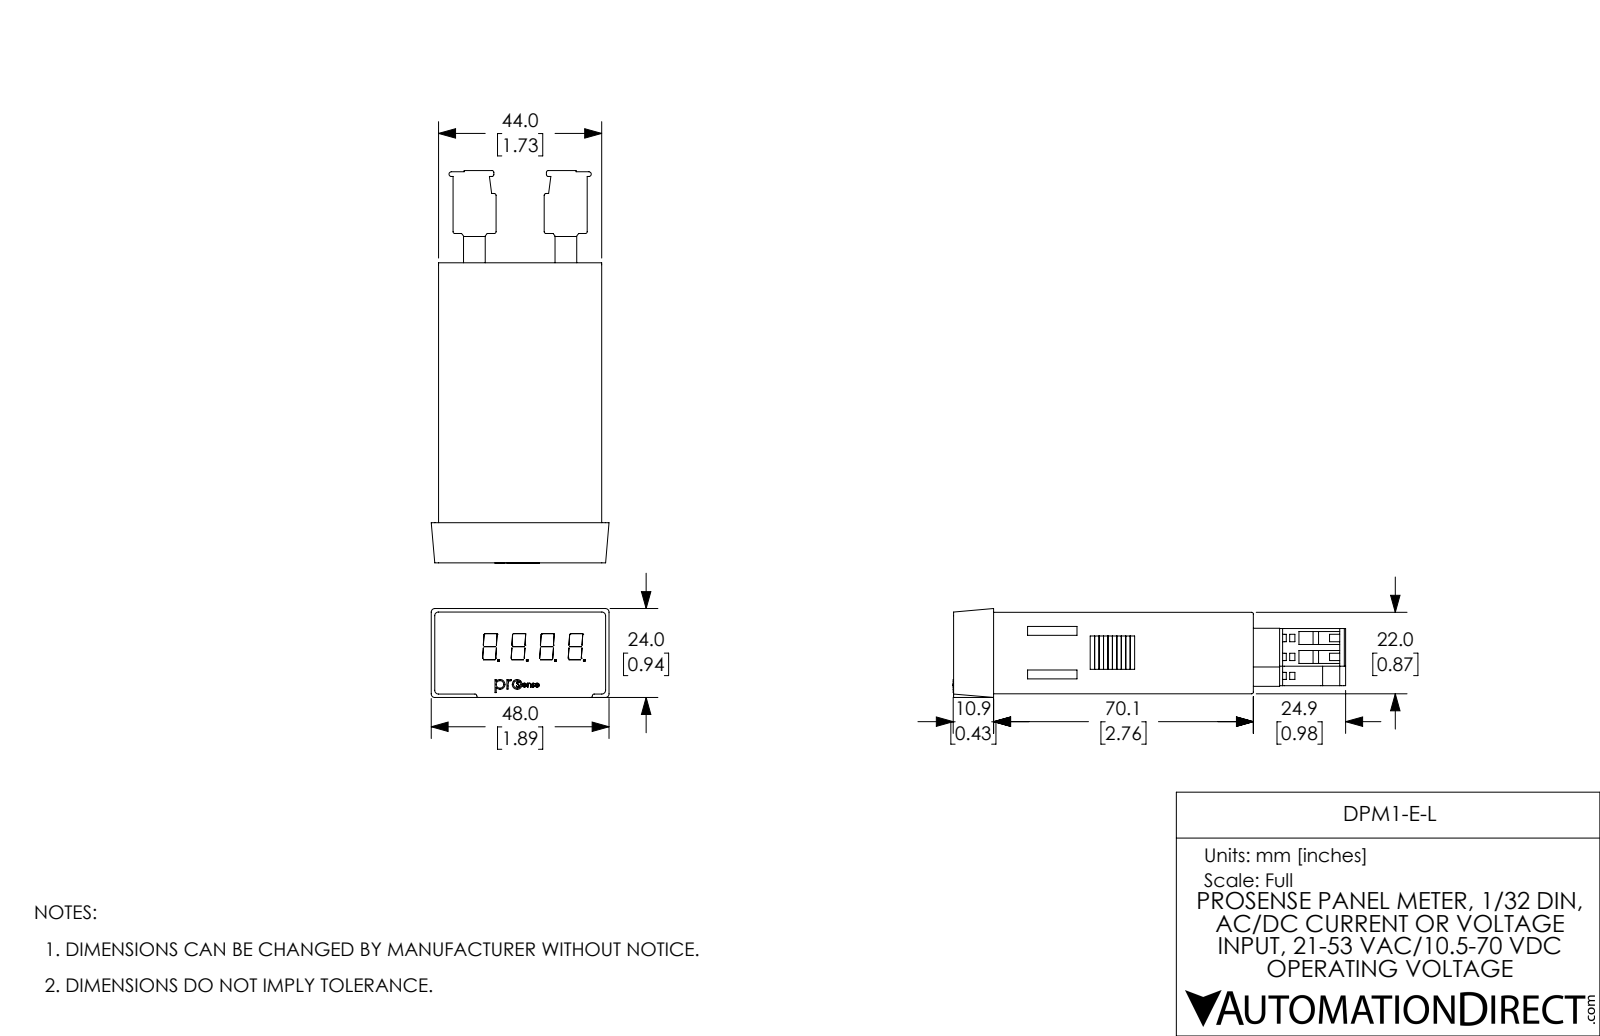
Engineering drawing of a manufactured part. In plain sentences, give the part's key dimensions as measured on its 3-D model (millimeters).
The part is named "DPM1-E-H coord a". Its 3-D file was written by "SolidWorks 2017 (AUTOMOTIVE_DESIGN)". It is 3 solids with 789 faces: 616 planar, 79 cylindrical and 94 other. Overall it measures 105.9 by 48 by 24 millimeters. Its volume is 30 690 cubic millimeters and its surface area 27 720 square millimeters. Round holes: 5 of diameter 2, 5 of diameter 3, 5 of diameter 3.9. Partial cylindrical surfaces (rounded edges, fillets, slot ends): 14 of radius 0.5, 5 of radius 3.1, 4 of radius 1, 2 of radius 0.6. The main face-to-face distances are 1.5, 20.5, 22, 19, 42.5, 44, 41, 1.3, 79.6, 11. The hole center spacings are 5, 5.1, 5, 5.1, 10.1, 24.7, 25, 25.
